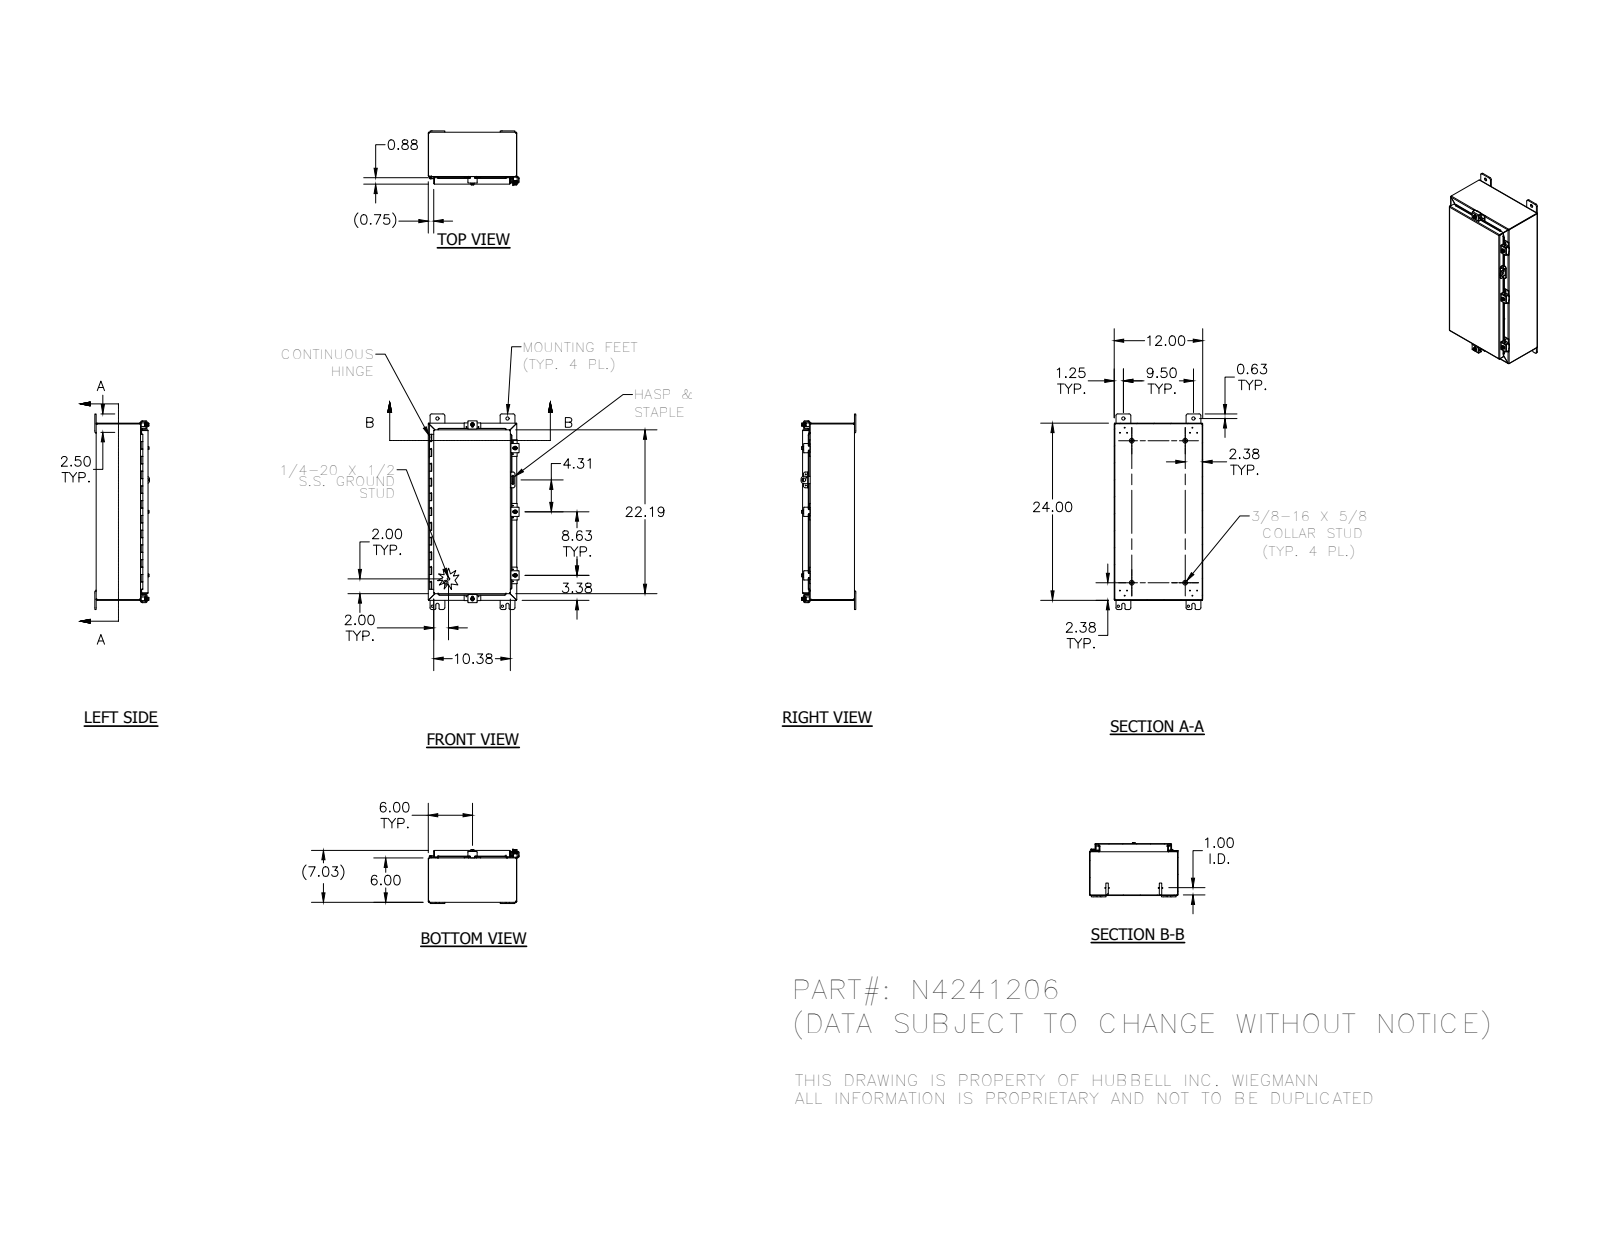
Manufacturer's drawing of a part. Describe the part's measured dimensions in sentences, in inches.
The part is named "328105P-1_1; 328105L_1; 328105T_1; N42412LID_1 (+8 more)". Its 3-D file was written by "SolidWorks 2014 (AUTOMOTIVE_DESIGN)". It is 42 solids with 1854 faces: 722 planar, 833 cylindrical and 299 other. Overall it measures 26.5 by 12.311 by 7.41 inches. Its volume is 101.4 cubic inches and its surface area 2 617 square inches. Round holes: 13 of diameter 0.11, 12 of diameter 0.12, 5 of diameter 0.211, 5 of diameter 0.281, 5 of diameter 0.3, 4 of diameter 0.313, 4 of diameter 0.438, 1 of diameter 0.125, 1 of diameter 0.156, 1 of diameter 0.5. Round bosses or shafts: 7 of diameter 0.25, 5 of diameter 0.52, 5 of diameter 0.5, 5 of diameter 0.35, 4 of diameter 0.625, 4 of diameter 0.33, 2 of diameter 0.115, 1 of diameter 0.337. Partial cylindrical surfaces (rounded edges, fillets, slot ends): 61 of radius 0.03, 37 of radius 0.062, 35 of radius 0.125, 31 of radius 0.25, 23 of radius 0.031, 23 of radius 0.105, 10 of radius 0.141, 8 of radius 0.063. The main face-to-face distances are 0.074, 6.959, 11.926, 6.885, 7.033, 5.926, 1.033, 23.926, 11.852, 12. The hole center spacings are 9.5, 0.876, 0.759, 0.839, 0.94, 0.969, 1.593, 1.995.
